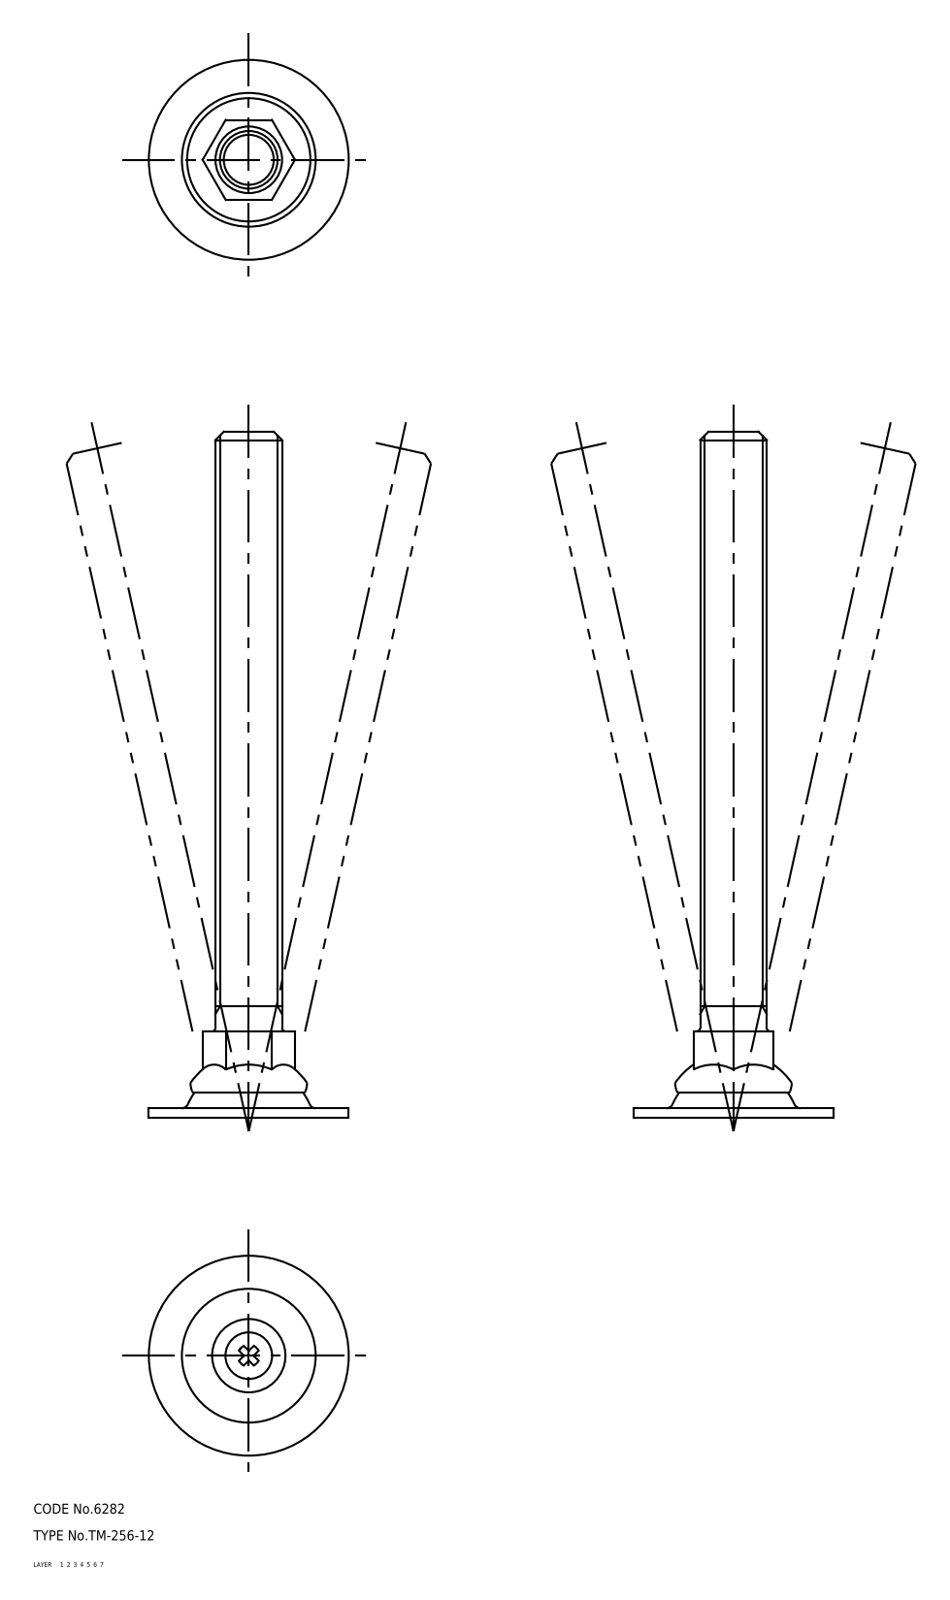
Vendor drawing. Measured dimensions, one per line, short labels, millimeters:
name: 67113284; 67113297; 67113310; 67113323
written by: CADfix (AUTOMOTIVE_DESIGN)
unit: mm
bodies: 4 solids, 72 faces (0 planar, 0 cylindrical, 72 other)
size: 126 × 60 × 60
volume: 48 772 mm³; area: 18 264 mm²
